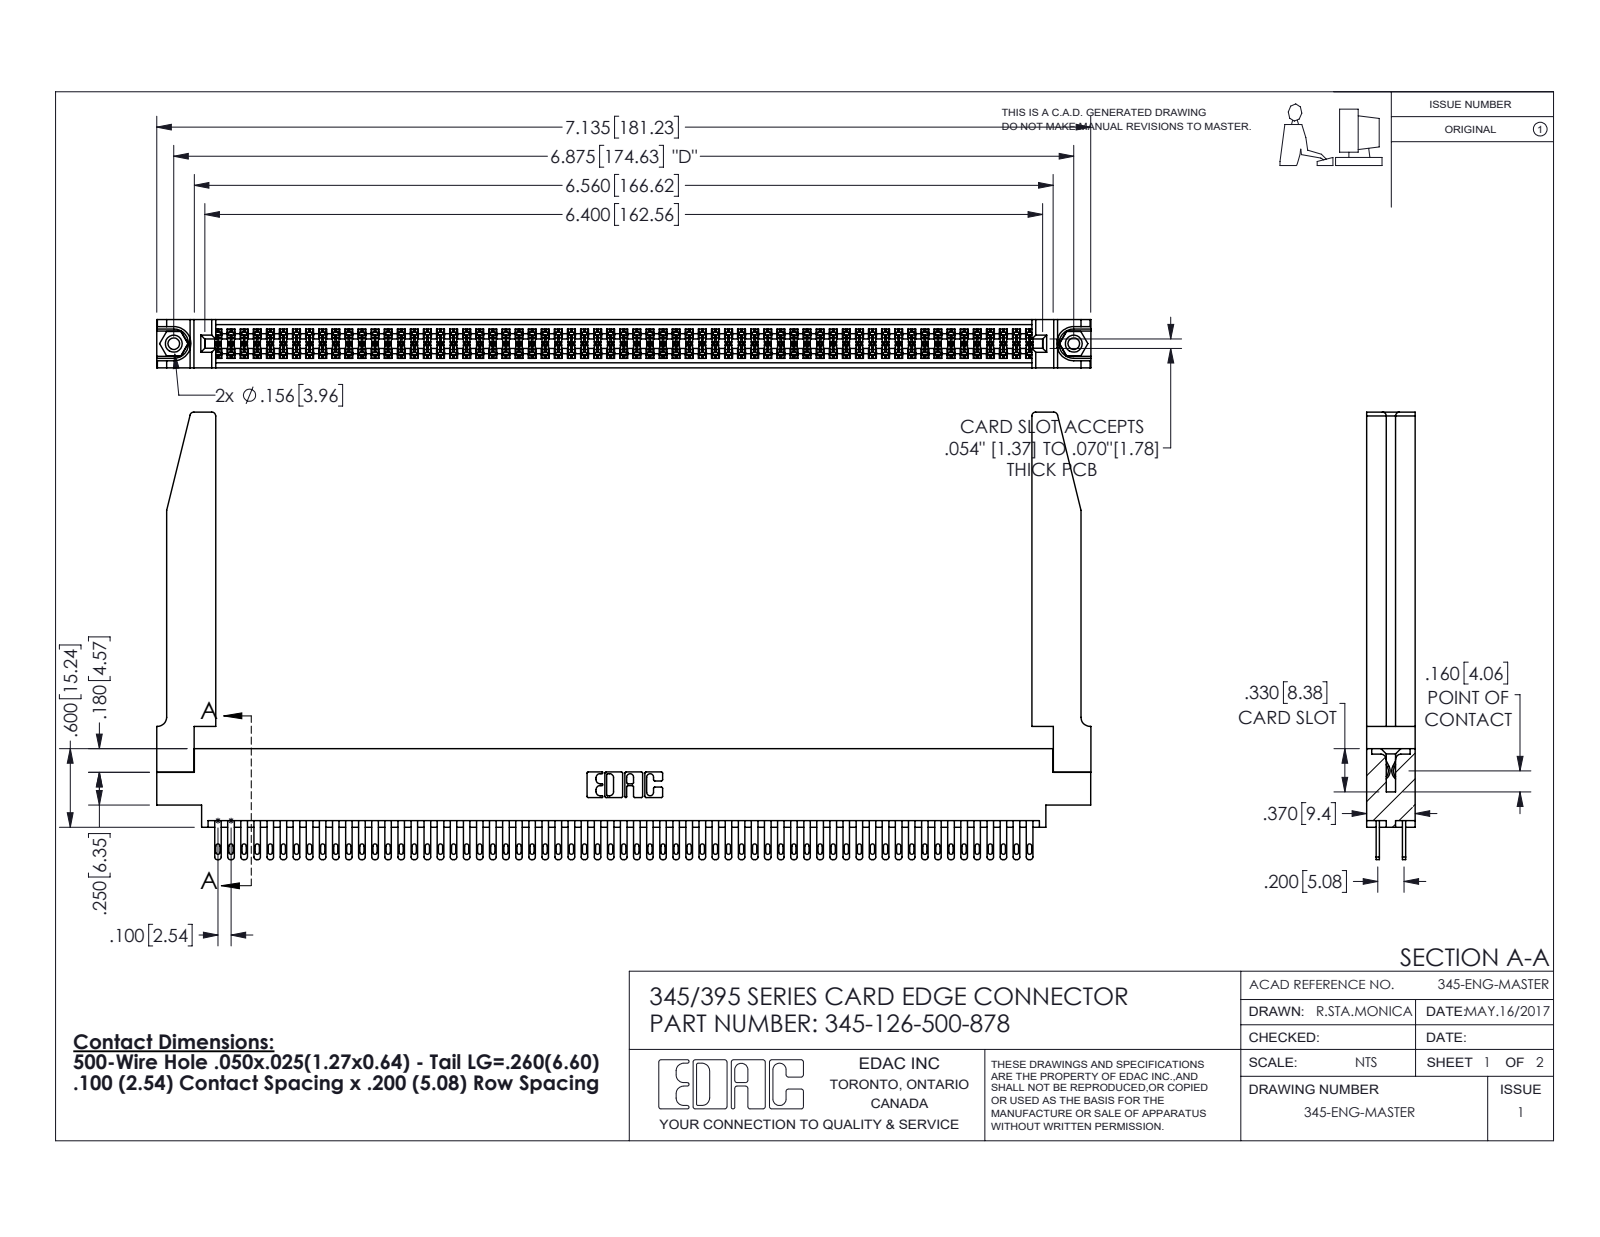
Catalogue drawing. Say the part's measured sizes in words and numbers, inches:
The part is named "345-126-500-878; 345-220-078_345-220-078; 345 Part_0.170 Offset - 0.156 Dia-TH; 345-250-001_345-250-001-102 (+1 more)". Its 3-D file was written by "SolidWorks 2016 (CONFIG_CONTROL_DESIGN)". It is 131 solids with 6160 faces: 3628 planar, 2480 cylindrical and 52 other. Overall it measures 7.136 by 3.417 by 0.37 inches. Its volume is 1.577 cubic inches and its surface area 54.85 square inches. Round holes: 2 of diameter 0.089, 2 of diameter 0.125, 2 of diameter 0.156, 1 of diameter 0.064. Round bosses or shafts: 2 of diameter 0.155. Partial cylindrical surfaces (rounded edges, fillets, slot ends): 189 of radius 0.006, 126 of radius 0.016, 126 of radius 0.02, 22 of radius 0.01, 8 of radius 0.03, 6 of radius 0.007, 6 of radius 0.031, 3 of radius 0.026. The main face-to-face distances are 0.072, 0.298, 0.37, 0.098, 0.272, 0.025, 0.2, 0.225, 0.175, 0.148. The hole center spacings are 0.27, 6.639, 6.875.
